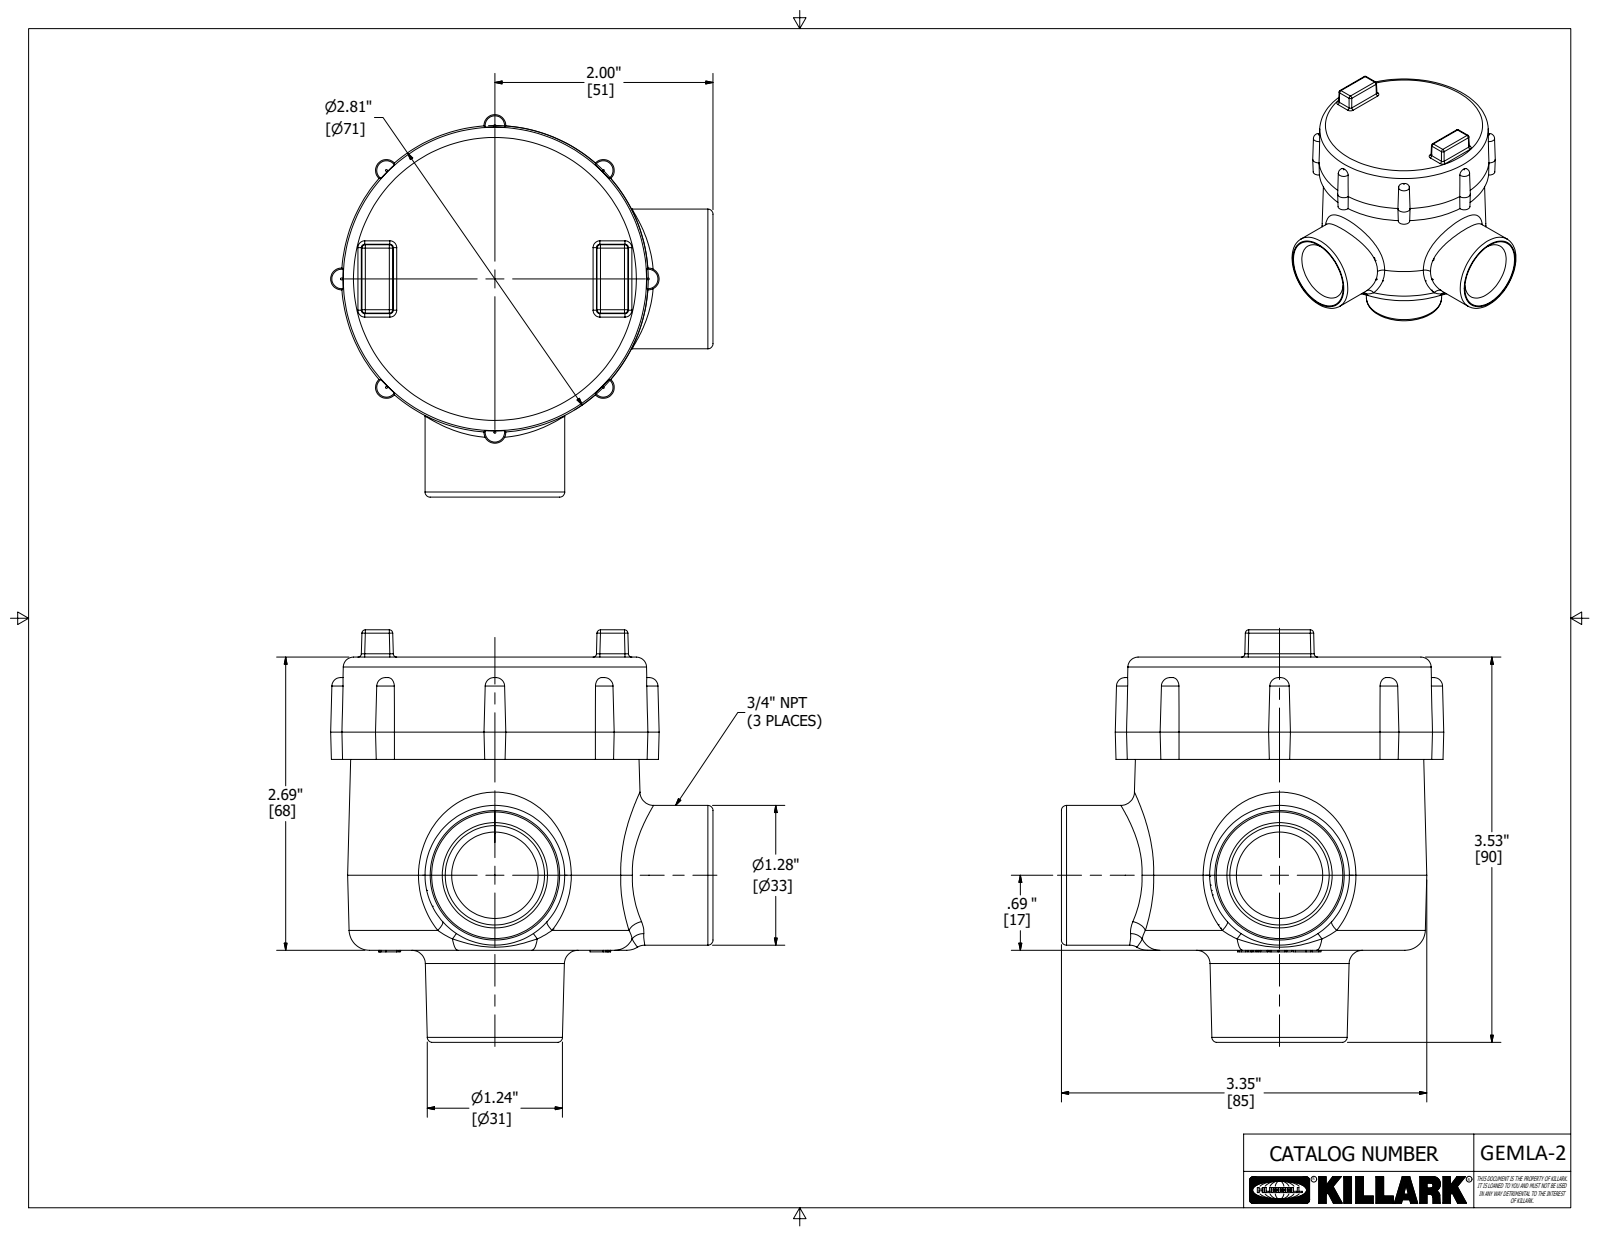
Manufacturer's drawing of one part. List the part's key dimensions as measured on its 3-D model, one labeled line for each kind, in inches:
Part name (STEP PRODUCT): GEMLA-2; 03975-2; 22491
STEP written by: Autodesk Inventor 2020 (AUTOMOTIVE_DESIGN)
Units: inches
Bodies: 2 solids, 583 faces (302 planar, 48 cylindrical, 233 other)
Overall size (bounding box): 3.781 × 3.506 × 3.506
Volume: 8.045 in³ · Surface area: 88.36 in²
Round holes (diameter × count): ⌀0.792 ×3, ⌀0.965 ×3, ⌀0.139 ×1, ⌀2.55 ×1
Round bosses / shafts (diameter × count): ⌀1.281 ×2, ⌀2.615 ×1
Partial cylindrical surfaces — rounded edges, fillets, slot ends (radius × count): R0.031 ×20, R0.047 ×8, R0.094 ×4, R0.185 ×1
Main face-to-face distances: 0.187, 2.5, 2.687, 2.313, 0.937, 1.75, 1.563, 0.75, 2.937, 2.75
